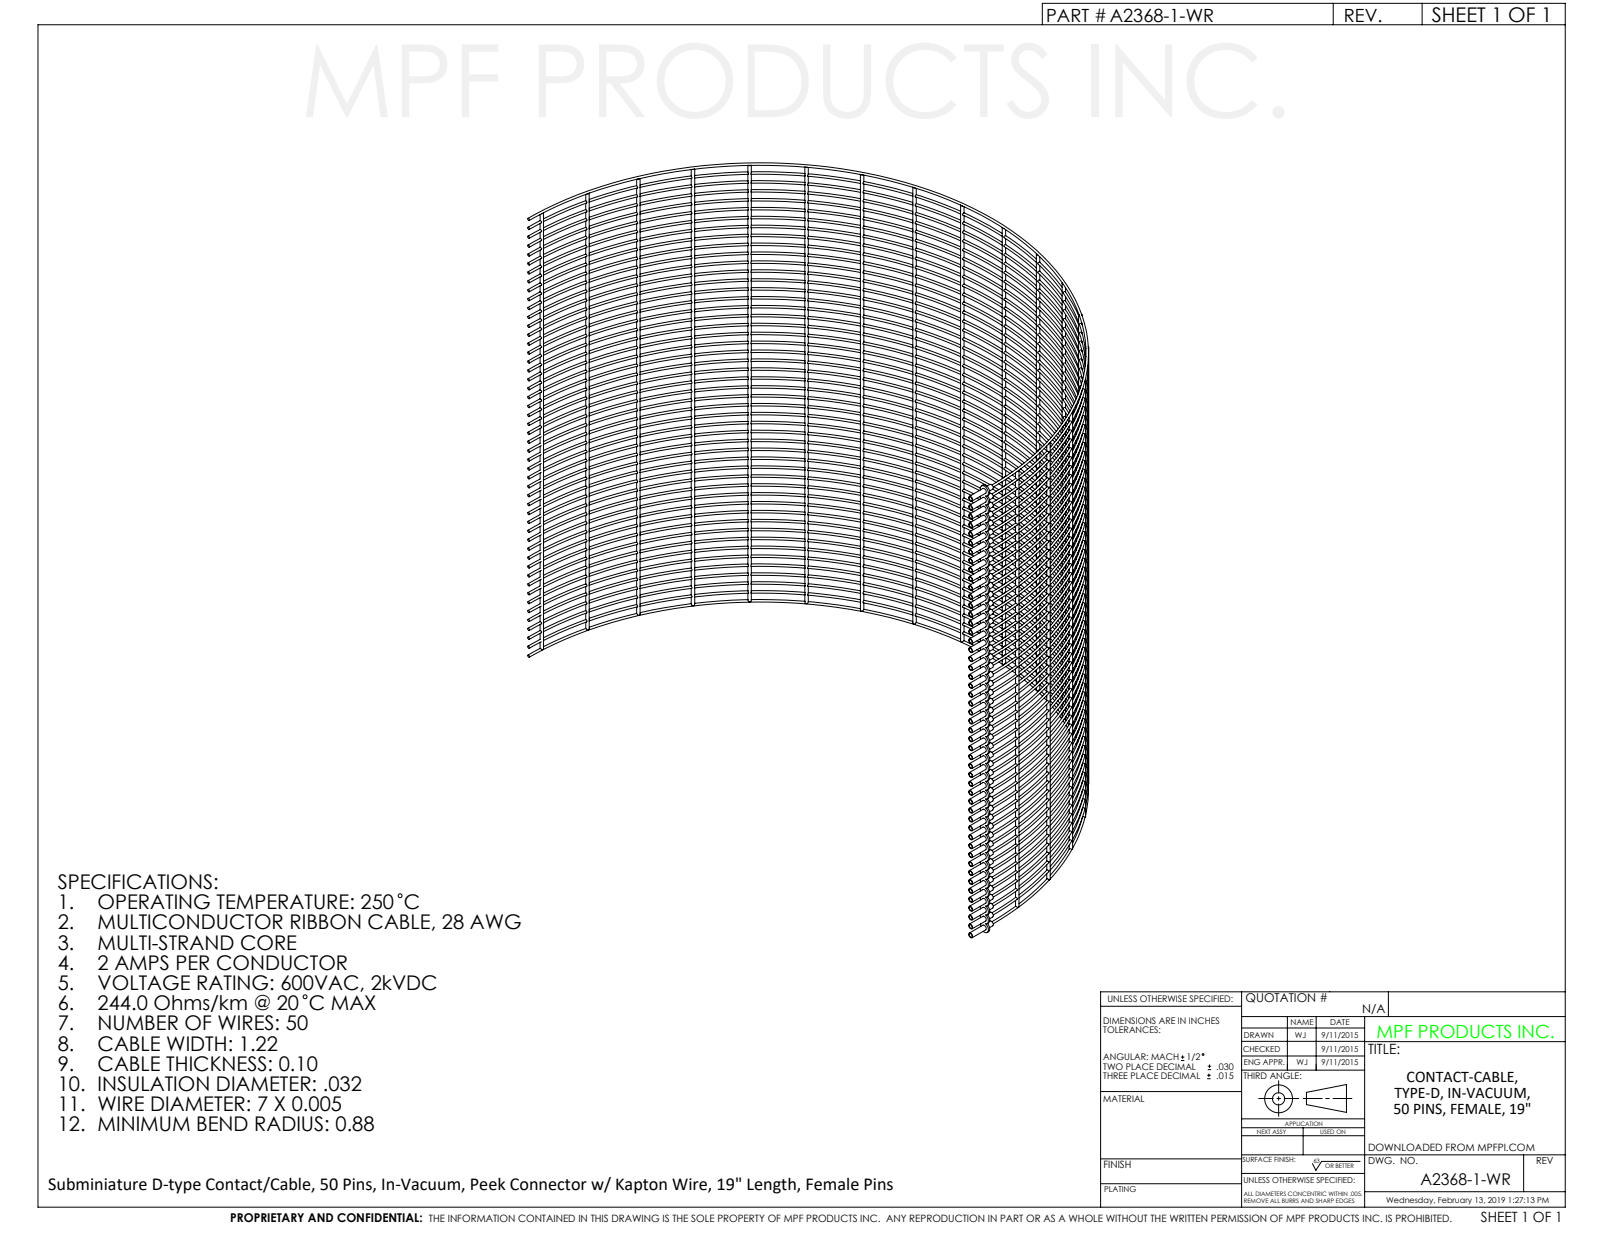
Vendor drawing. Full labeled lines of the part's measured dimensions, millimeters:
Part name (STEP PRODUCT): A2368-1-WR
STEP written by: SolidWorks 2012 (CONFIG_CONTROL_DESIGN)
Units: millimetres
Bodies: 1 solid, 2706 faces (275 planar, 485 cylindrical, 1946 other)
Overall size (bounding box): 154 × 127.1 × 83.3
Volume: 4 590 mm³ · Surface area: 28 400 mm²
Round holes (diameter × count): ⌀1 ×50
Round bosses / shafts (diameter × count): ⌀1.3 ×50, ⌀2.7 ×49, ⌀0.8 ×18
Partial cylindrical surfaces — rounded edges, fillets, slot ends (radius × count): R1.3 ×1
Main face-to-face distances: 0.5, 1.9, 2.3, 4, 2.2, 1.7, 6.8, 5, 4.5, 2.8
Hole centre spacings: 2.5, 5.1, 7.6, 10.2, 12.7, 15.2, 17.8, 20.3
